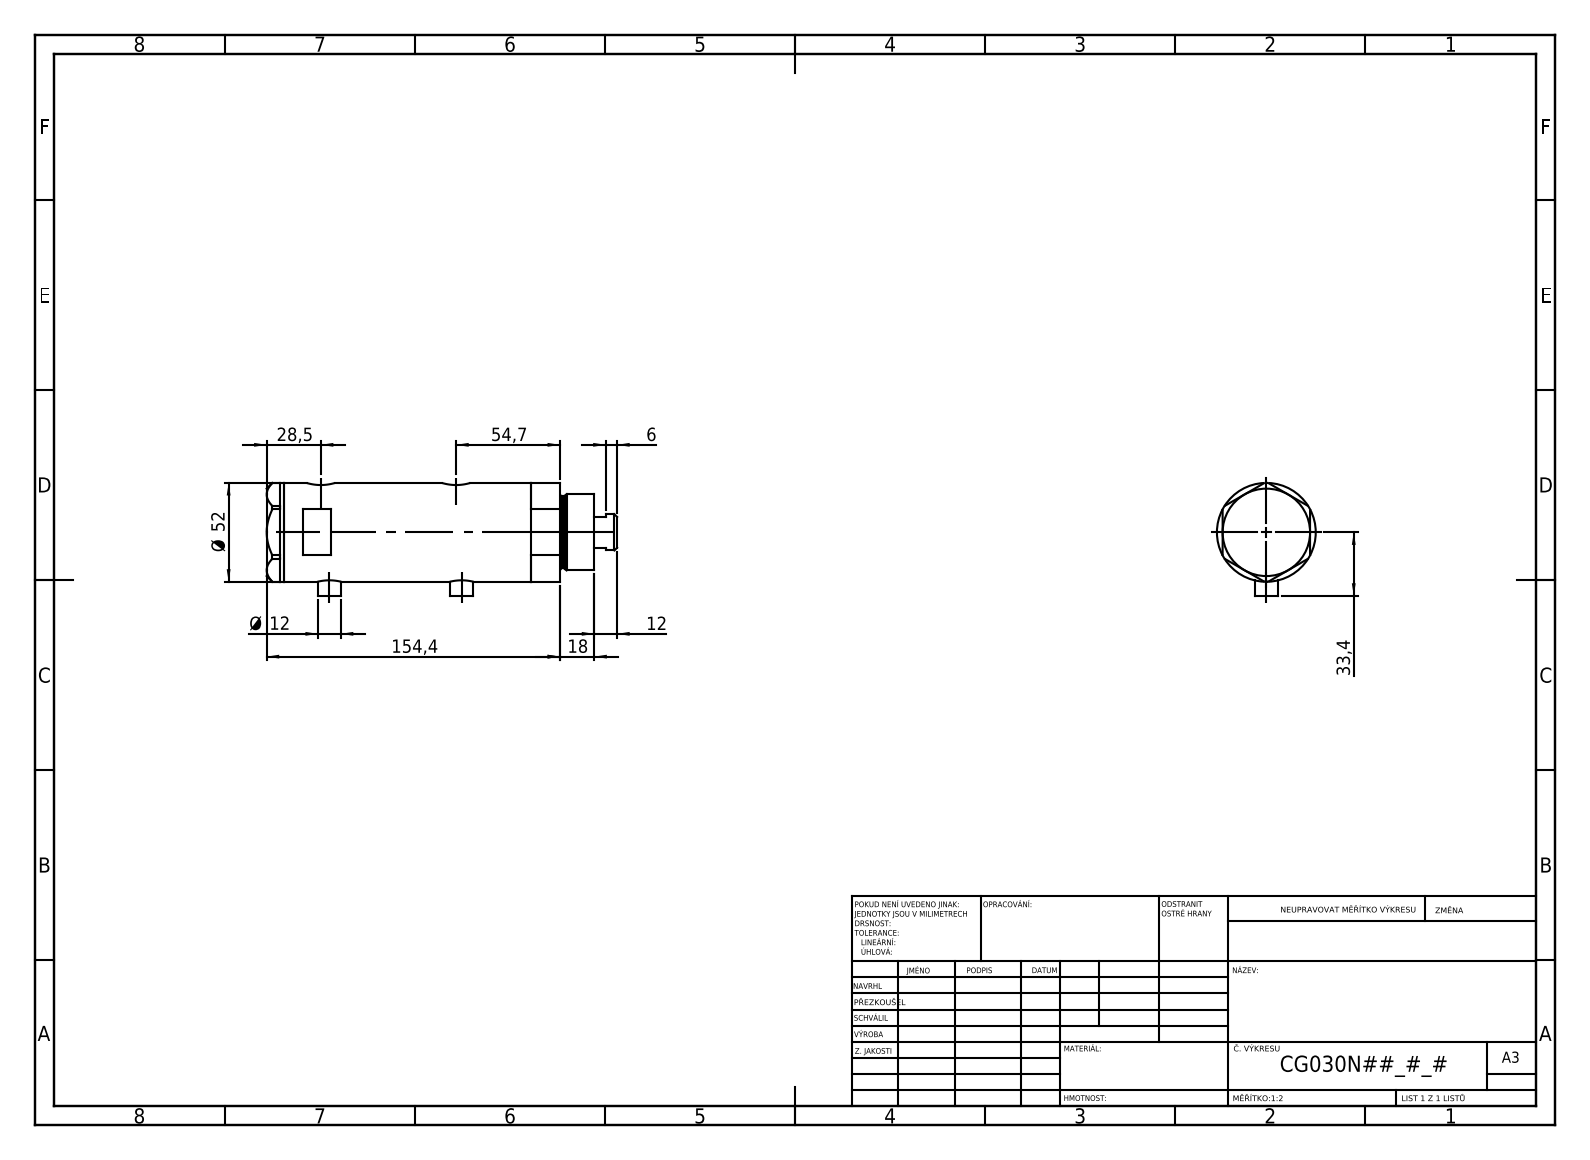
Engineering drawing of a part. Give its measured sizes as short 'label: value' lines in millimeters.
name: V270CG_VC; V270CG_BACK; V270CG_FRONT; V270CG_MIDDLE
written by: SolidWorks 2019 (CONFIG_CONTROL_DESIGN)
unit: mm
bodies: 4 solids, 134 faces (65 planar, 49 cylindrical, 20 other)
size: 184.4 × 59.4 × 52
volume: 331 757 mm³; area: 77 131 mm²
holes: 2× ⌀9.64, 2× ⌀12.5, 2× ⌀15, 1× ⌀6.5, 1× ⌀20, 1× ⌀21.5, 1× ⌀30, 1× ⌀33, 1× ⌀44
bosses: 2× ⌀12, 1× ⌀52, 1× ⌀40, 1× ⌀38, 1× ⌀19
face distances: 93.5, 23.8, 69.7, 9, 32.8, 102.5, 46, 138.9, 129.9, 106.1
hole spacings: 2.9, 4.5, 66.7, 69.6, 71.2, 74.1
